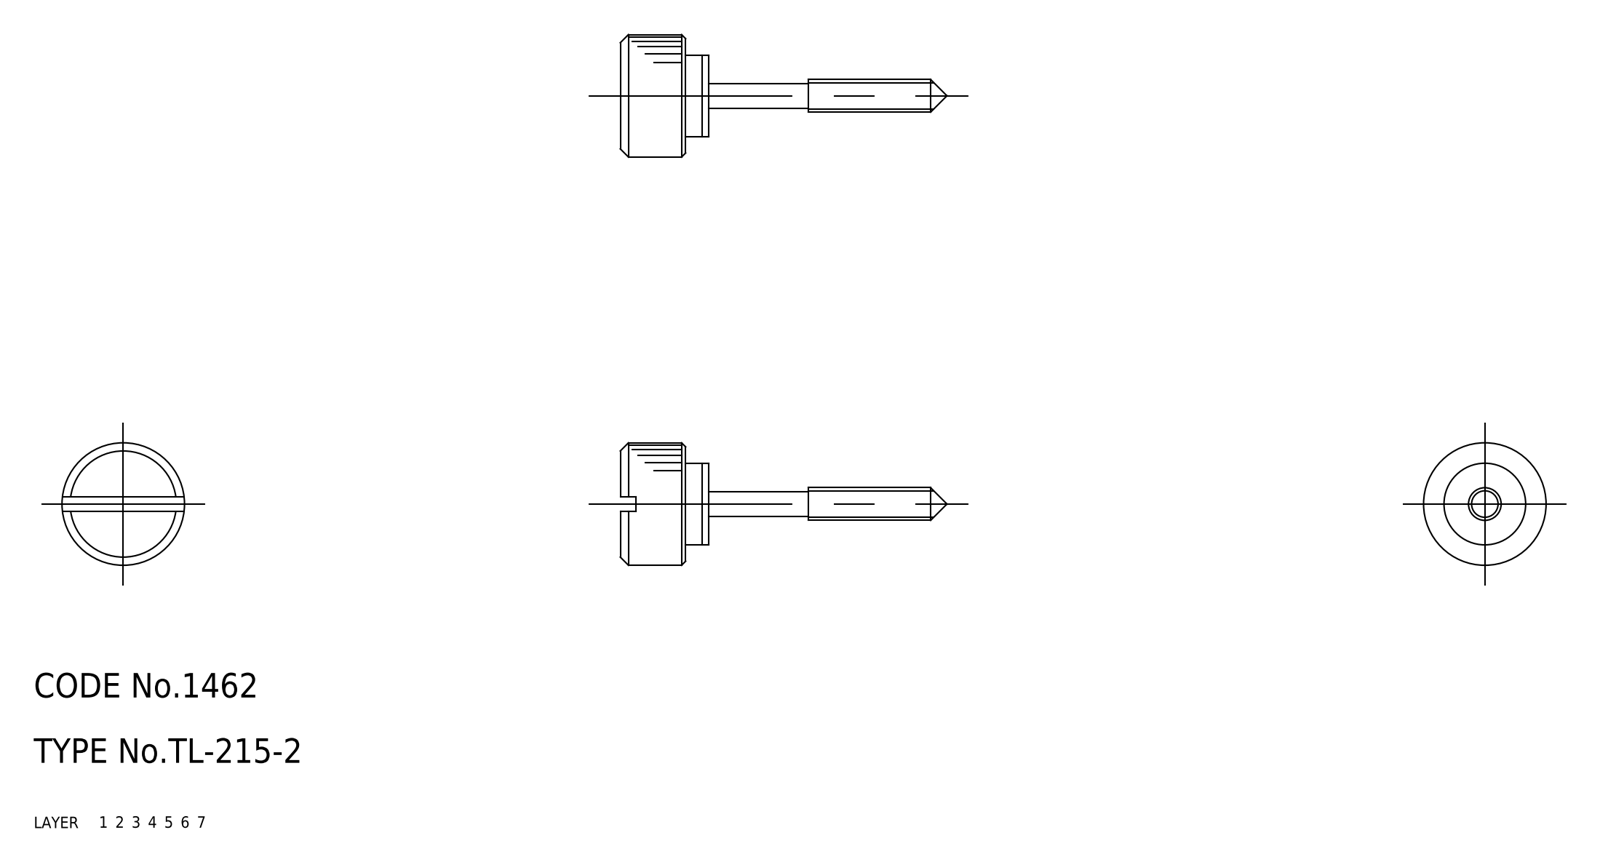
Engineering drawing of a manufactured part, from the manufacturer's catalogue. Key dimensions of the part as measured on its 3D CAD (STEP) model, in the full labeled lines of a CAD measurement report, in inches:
Part name (STEP PRODUCT): washer; knob; TL_215_2_25786_36
STEP written by: CADfix (AUTOMOTIVE_DESIGN)
Units: inches
Bodies: 2 solids, 38 faces (0 planar, 0 cylindrical, 38 other)
Overall size (bounding box): 1.575 × 0.591 × 0.591
Volume: 0.112 in³ · Surface area: 2.009 in²
